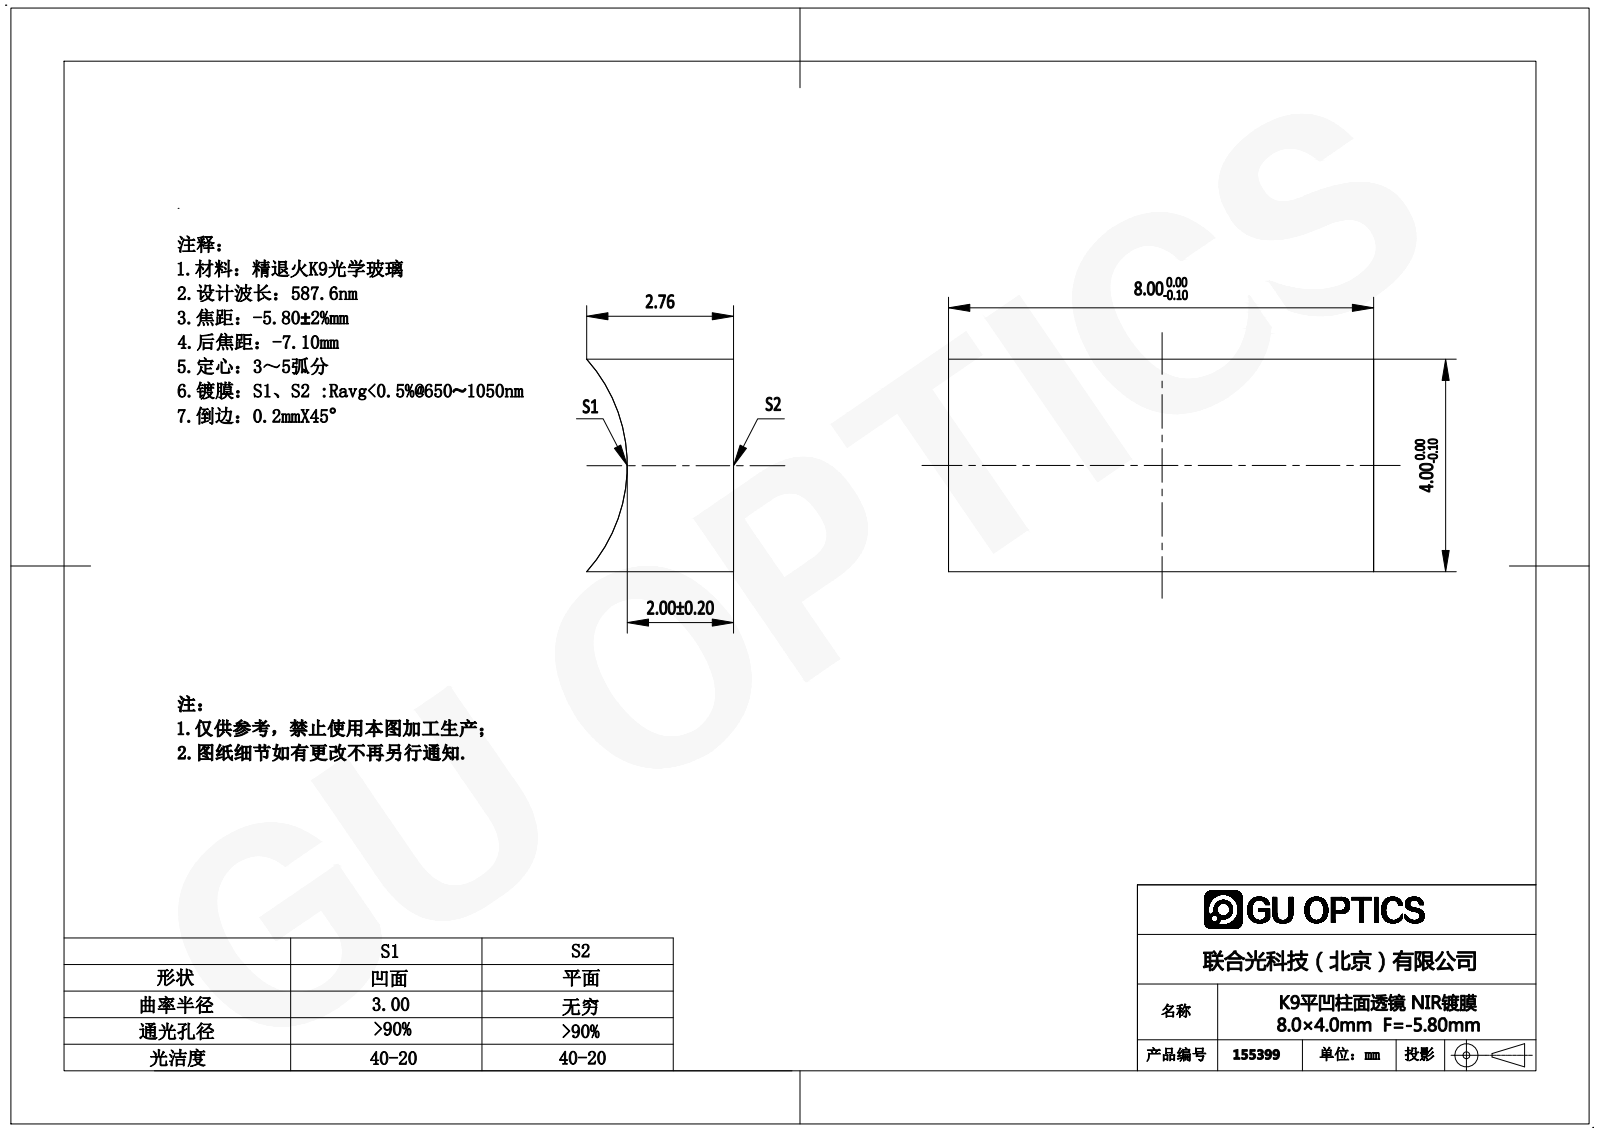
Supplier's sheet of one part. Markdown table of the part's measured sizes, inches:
| quantity | value |
| --- | --- |
| part name | 155333 |
| STEP written by | SolidWorks 2016 (AUTOMOTIVE_DESIGN) |
| units | inches |
| bodies | 1 solid, 6 faces (5 planar, 1 cylindrical, 0 other) |
| overall size | 0.315 × 0.157 × 0.109 |
| volume | 0.004 in³ |
| surface area | 0.2 in² |
| partial cylindrical surfaces (radius × count) | 0.118 × 1 |
| main face-to-face distances | 0.157, 0.315 |
